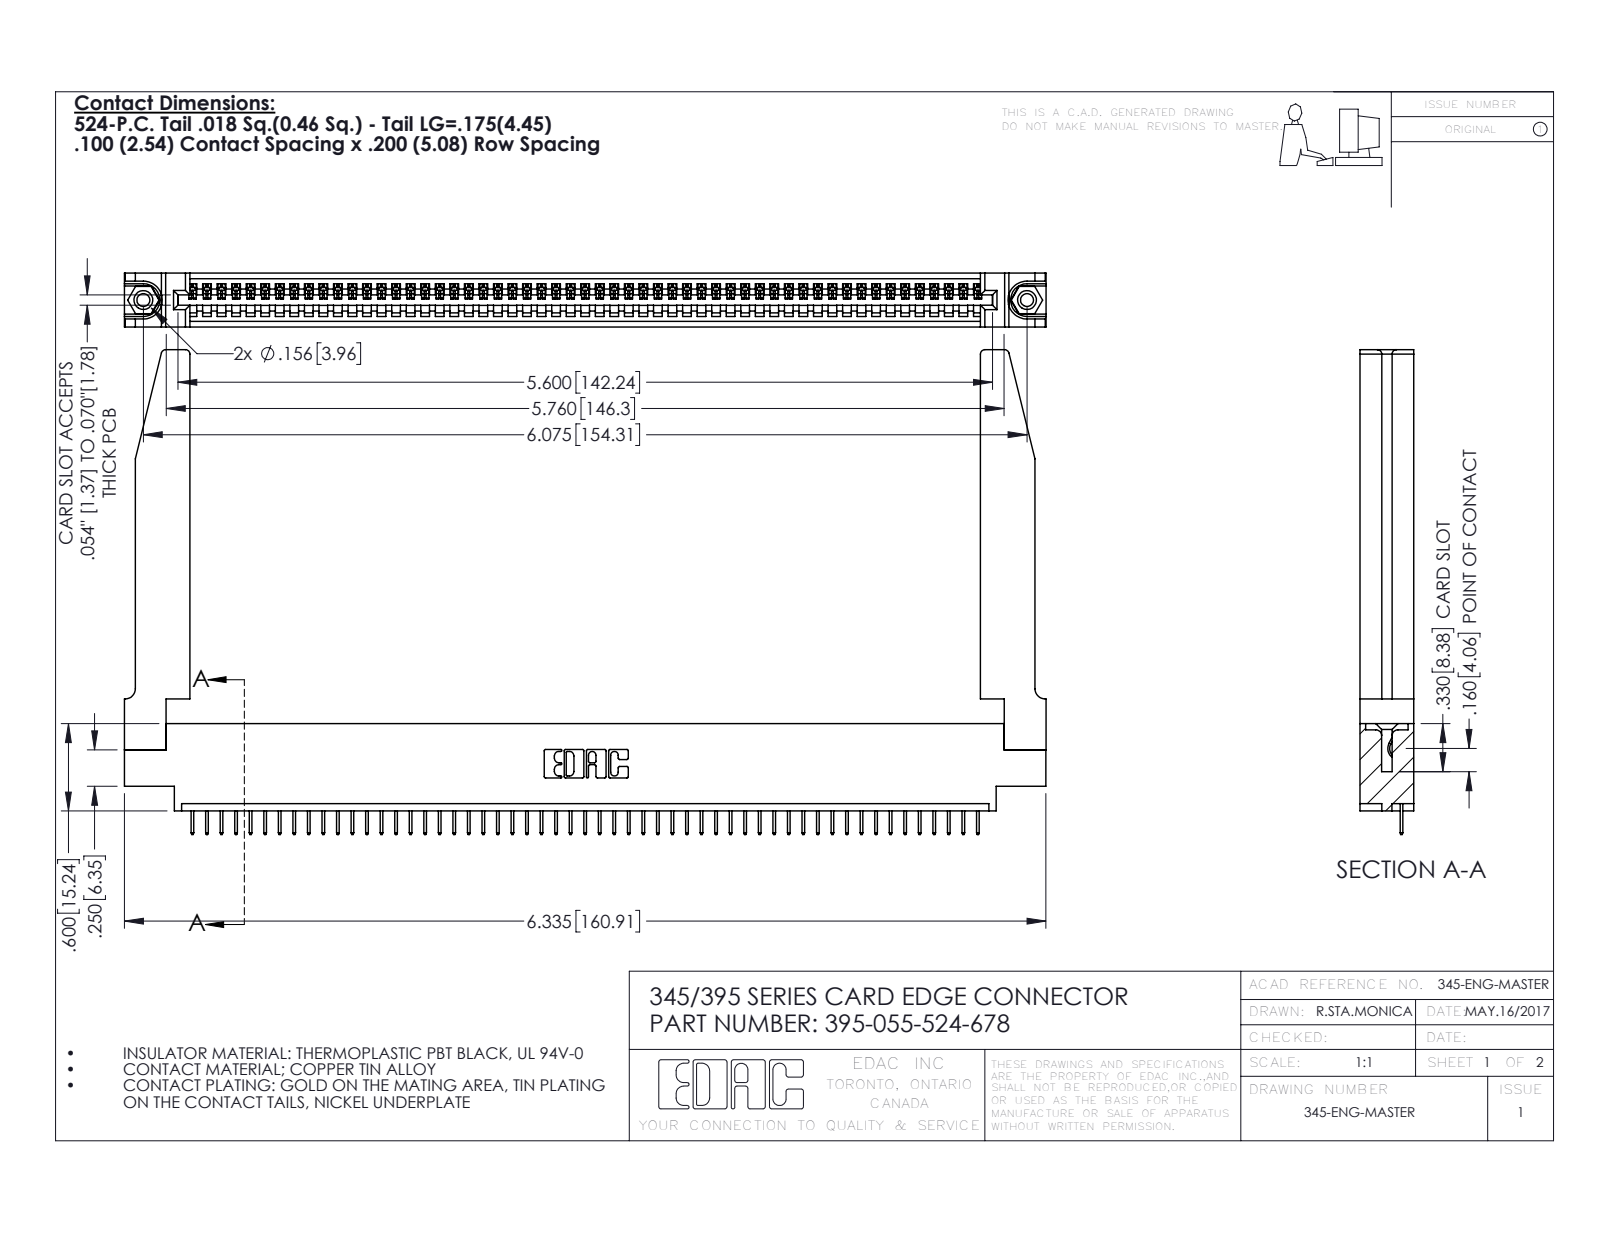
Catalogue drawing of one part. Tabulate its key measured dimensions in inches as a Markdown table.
| quantity | value |
| --- | --- |
| part name | 395-055-524-678; 345-292-001_345-293-124; 345-220-078_345-220-078; 345-250-001_345-250-001-102 (+1 more) |
| STEP written by | SolidWorks 2016 (CONFIG_CONTROL_DESIGN) |
| units | inches |
| bodies | 60 solids, 3774 faces (2756 planar, 966 cylindrical, 52 other) |
| overall size | 6.336 × 3.332 × 0.37 |
| volume | 1.393 in³ |
| surface area | 41.03 in² |
| round holes (diameter × count) | 0.089 × 2, 0.125 × 2, 0.156 × 2, 0.064 × 1 |
| round bosses / shafts (diameter × count) | 0.155 × 2 |
| partial cylindrical surfaces (radius × count) | 0.006 × 110, 0.01 × 22, 0.03 × 8, 0.007 × 6, 0.031 × 6, 0.026 × 3, 0.031 × 2, 0.04 × 2 |
| main face-to-face distances | 0.37, 0.072, 0.298, 0.098, 0.272, 0.025, 0.2, 0.225, 0.072, 0.148 |
| hole center spacings | 0.27, 5.839, 6.075 |
